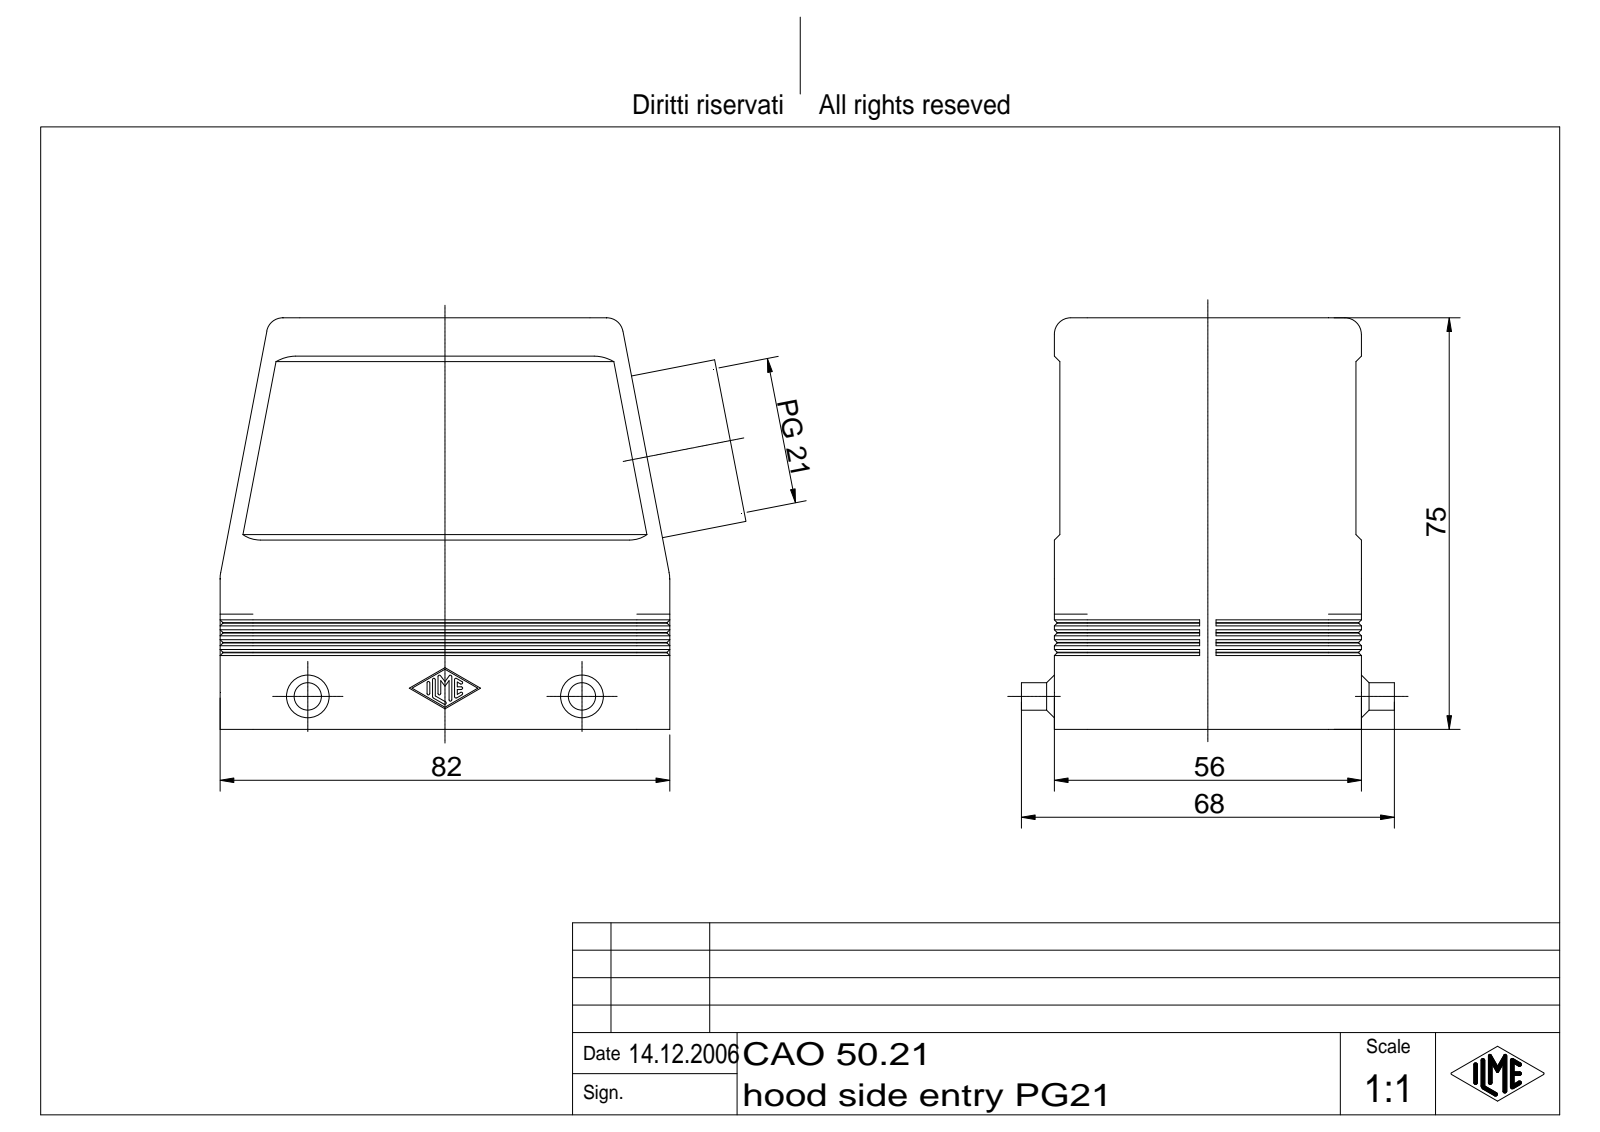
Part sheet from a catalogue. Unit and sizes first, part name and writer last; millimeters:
Units: millimetres
Overall size (bounding box): 95.9 × 75 × 68
Round holes (diameter × count): ⌀2.46 ×4, ⌀3.5 ×4, ⌀24.78 ×1, ⌀26.78 ×1
Round bosses / shafts (diameter × count): ⌀5 ×2, ⌀30 ×1
Partial cylindrical surfaces — rounded edges, fillets, slot ends (radius × count): R0.25 ×14, R6 ×10, R2 ×8, R3 ×8, R5.5 ×2
Main face-to-face distances: 3, 53, 50, 56, 2, 1, 52, 55, 11.25, 70.75
Hole centre spacings: 16, 66, 67.91
Volume: 77 842 mm³ · Surface area: 48 678 mm²
Bodies: 1 solid, 457 faces (169 planar, 134 cylindrical, 154 other)
Part name (STEP PRODUCT): CAO 50.21
STEP written by: Autodesk Inventor 7 (AUTOMOTIVE_DESIGN)
